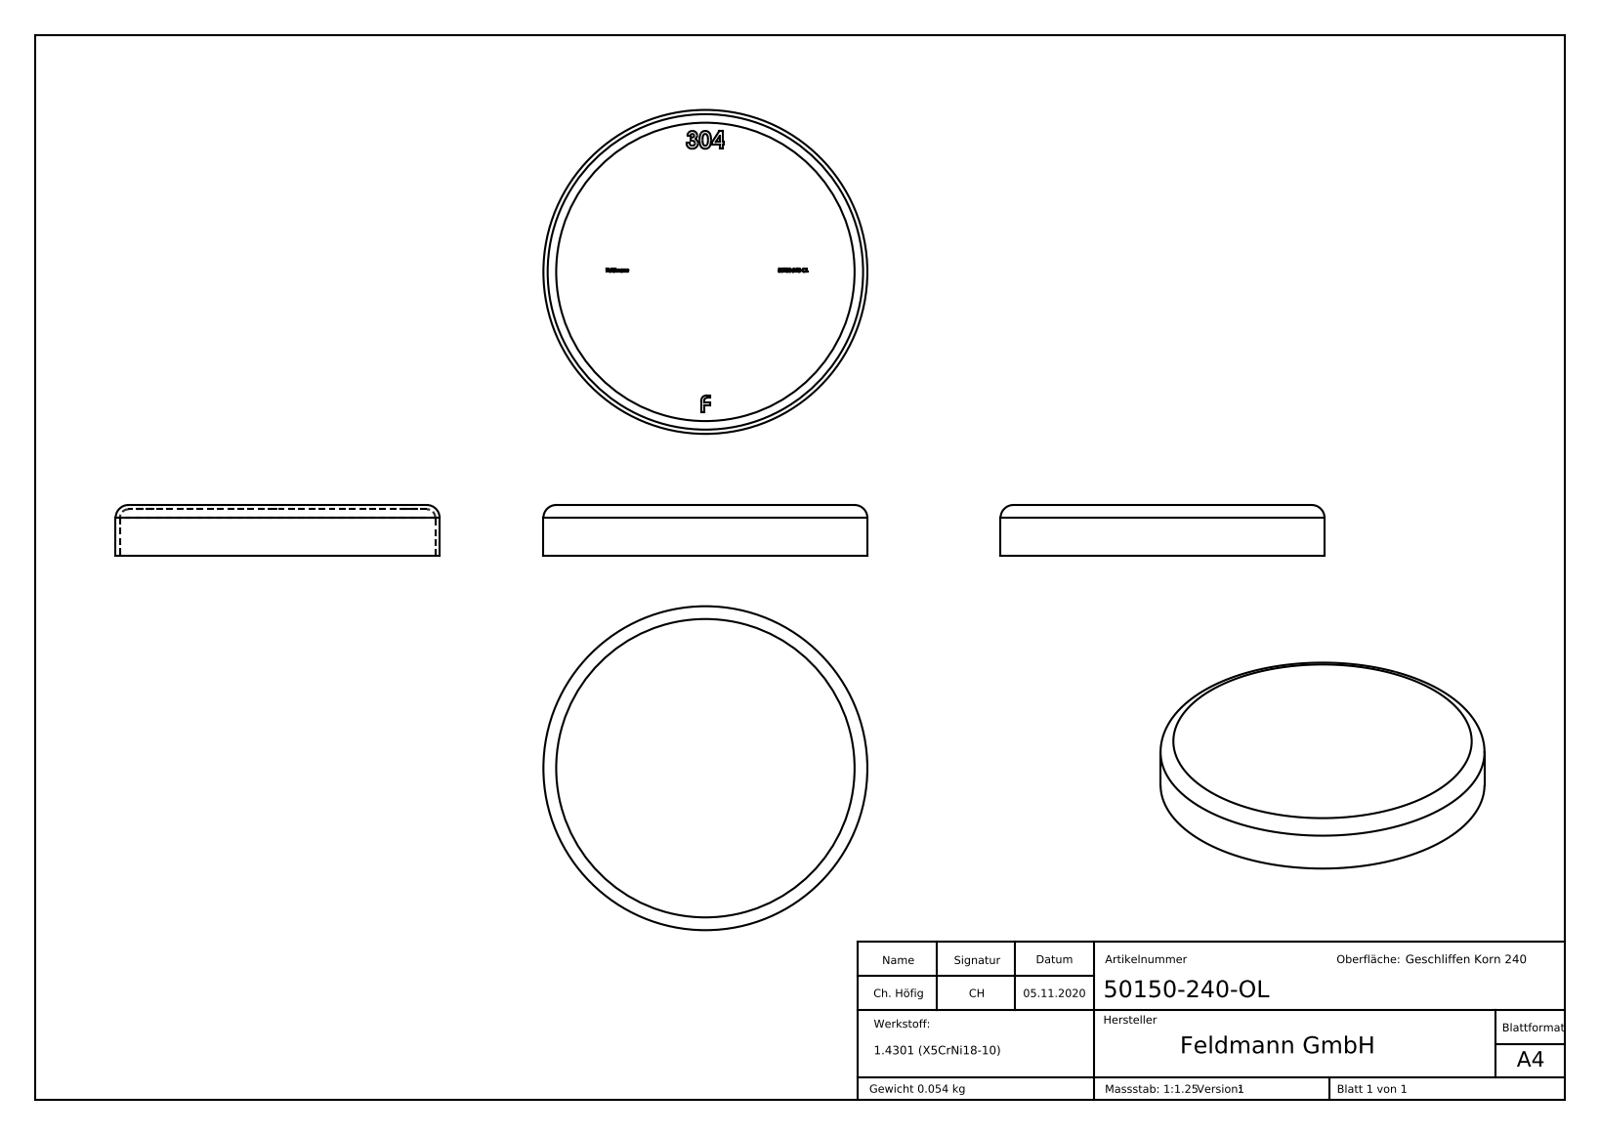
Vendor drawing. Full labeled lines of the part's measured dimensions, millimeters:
Part name (STEP PRODUCT): 50150-240-OL
STEP written by: SolidWorks 2018 (CONFIG_CONTROL_DESIGN)
Units: millimetres
Bodies: 1 solid, 307 faces (169 planar, 4 cylindrical, 134 other)
Overall size (bounding box): 76 × 76 × 12
Volume: 6 870 mm³ · Surface area: 13 996 mm²
Round holes (diameter × count): ⌀74 ×1
Round bosses / shafts (diameter × count): ⌀76 ×1
Main face-to-face distances: 1, 11, 12, 11.1, 0.9, 0.71, 5, 4.29, 0.58, 0.69
